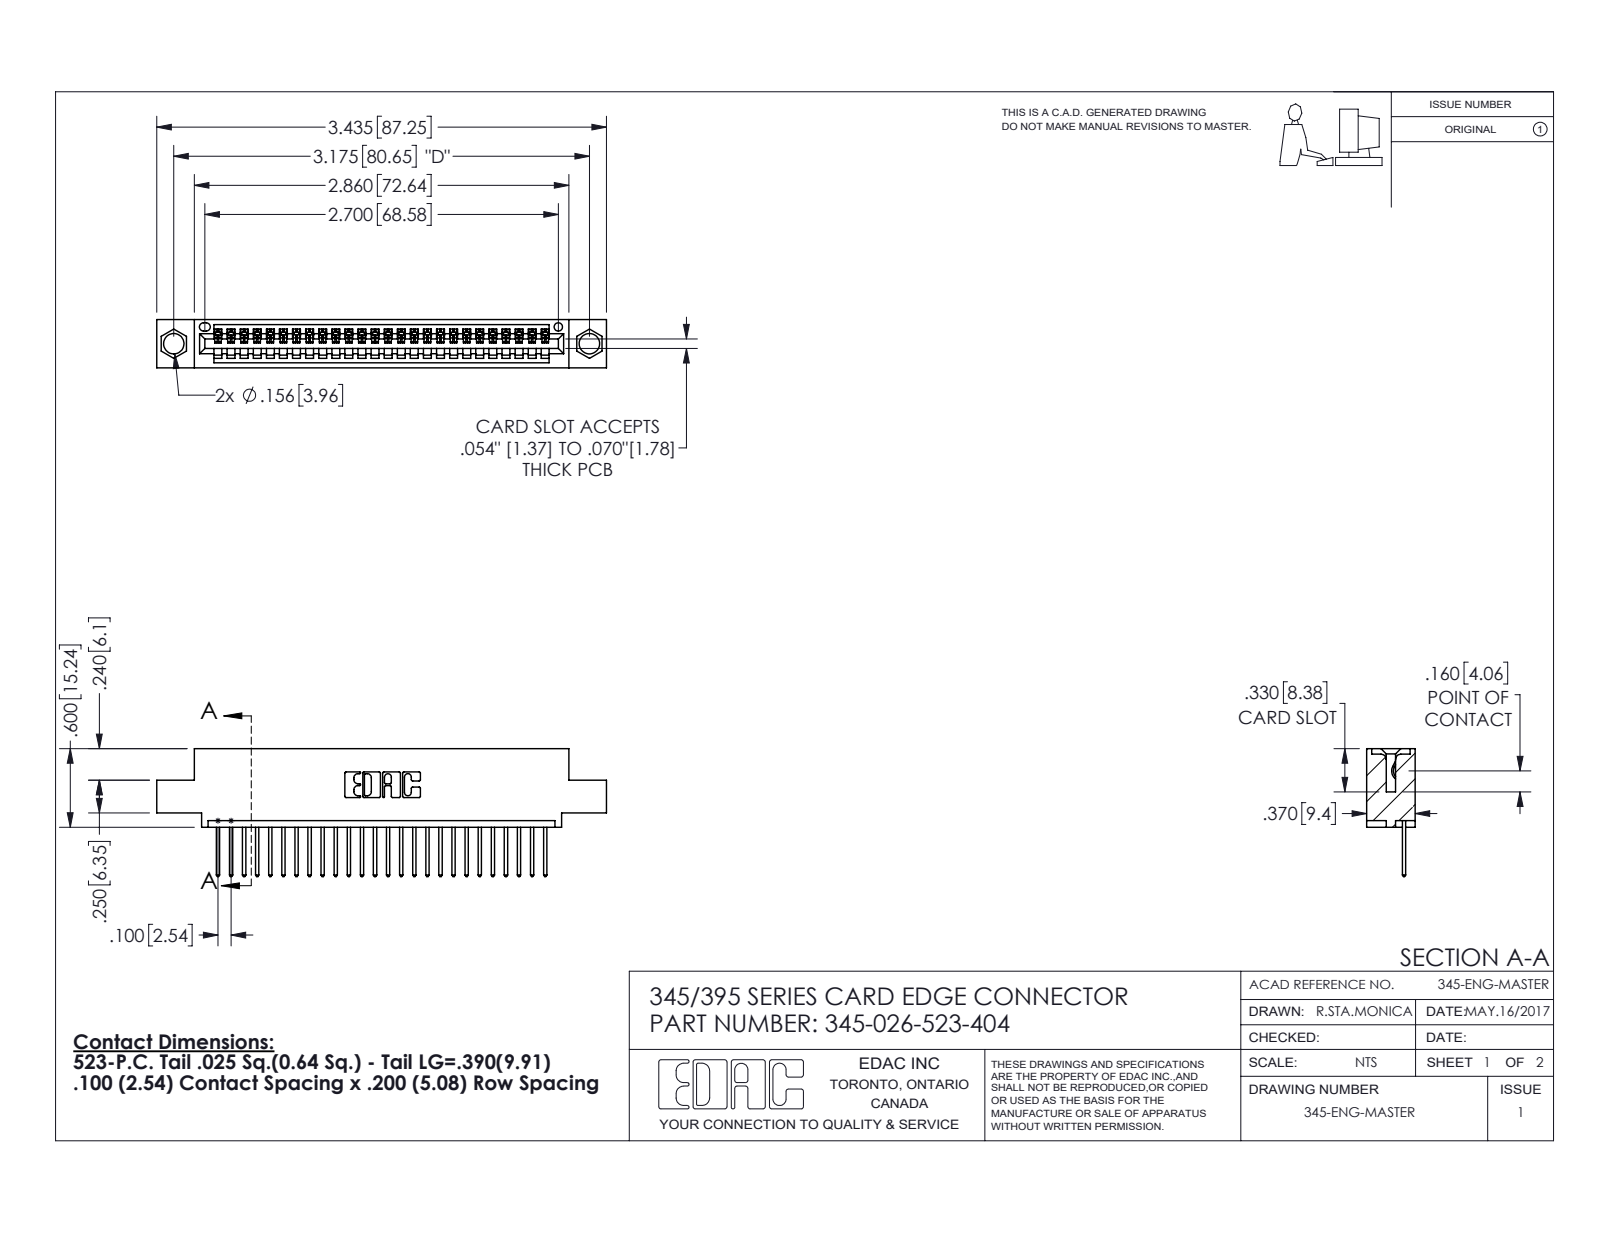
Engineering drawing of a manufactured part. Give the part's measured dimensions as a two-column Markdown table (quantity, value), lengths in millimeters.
| quantity | value |
| --- | --- |
| part name | 345-026-523-404; 345 Part_0.110 Offset - 0.156 Dia-TH; 345-292-001_345-293-123 |
| STEP written by | SolidWorks 2016 (CONFIG_CONTROL_DESIGN) |
| units | millimeters |
| bodies | 27 solids, 1638 faces (1124 planar, 514 cylindrical, 0 other) |
| overall size | 87.2 × 24.8 × 9.4 |
| volume | 7 980 mm³ |
| surface area | 10 310 mm² |
| round holes (diameter × count) | 4 × 2, 1.6 × 1 |
| partial cylindrical surfaces (radius × count) | 0.2 × 52, 0.3 × 52, 0.3 × 22, 0.2 × 6, 0.8 × 6, 0.7 × 3, 0.8 × 2, 1 × 2 |
| main face-to-face distances | 7.6, 1.8, 9.4, 5.1, 2.5, 6.9, 0.6, 5.7, 3.8, 1.8 |
| hole center spacings | 6.9, 74.7, 80.6 |
